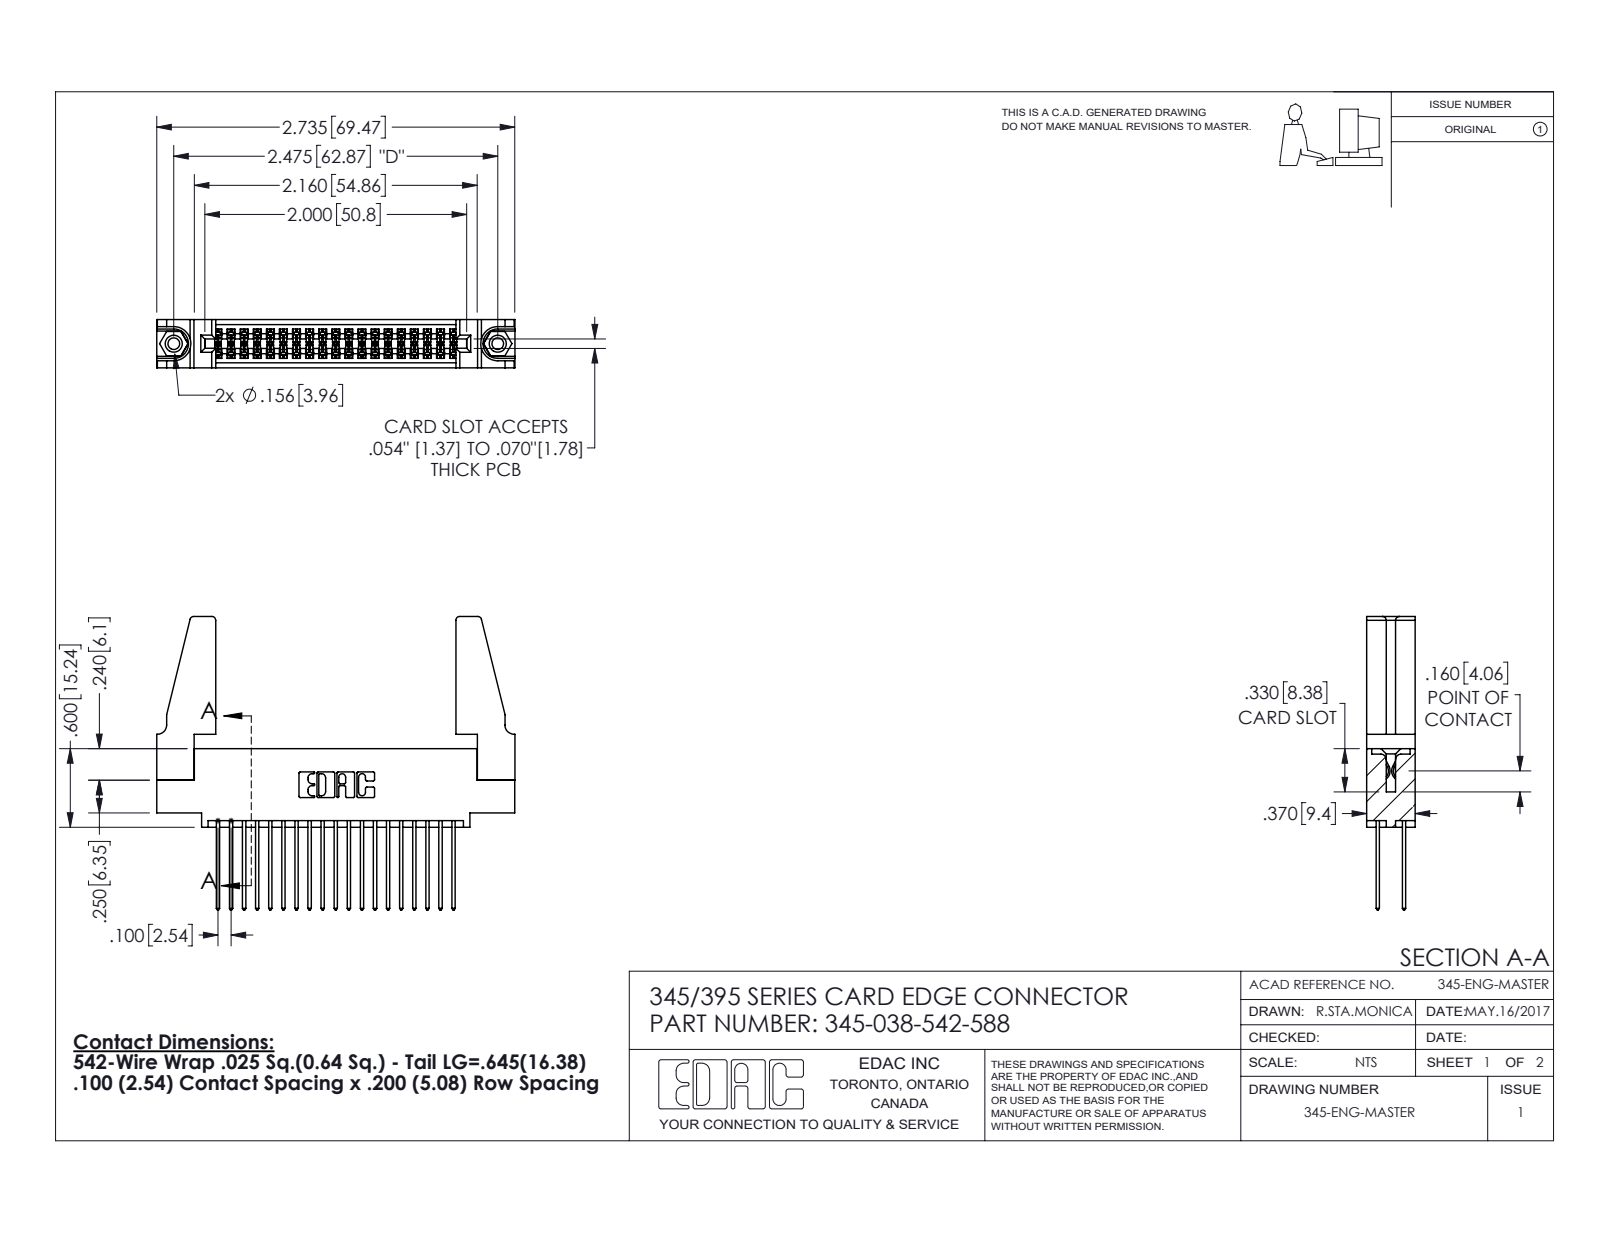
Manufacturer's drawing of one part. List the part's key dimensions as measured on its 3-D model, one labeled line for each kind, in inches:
Part name (STEP PRODUCT): 345-250-001_345-250-001-102; 345-220-078_345-220-088; 345 Part_0.110 Offset - 0.156 Dia-TH; 345-038-542-588 (+1 more)
STEP written by: SolidWorks 2016 (CONFIG_CONTROL_DESIGN)
Units: inches
Bodies: 43 solids, 2154 faces (1410 planar, 728 cylindrical, 16 other)
Overall size (bounding box): 2.736 × 2.242 × 0.37
Volume: 0.604 in³ · Surface area: 20.79 in²
Round holes (diameter × count): ⌀0.089 ×2, ⌀0.125 ×2, ⌀0.156 ×2, ⌀0.064 ×1
Round bosses / shafts (diameter × count): ⌀0.155 ×2
Partial cylindrical surfaces — rounded edges, fillets, slot ends (radius × count): R0.006 ×57, R0.01 ×38, R0.01 ×22, R0.03 ×8, R0.007 ×6, R0.031 ×6, R0.026 ×3, R0.014 ×2
Main face-to-face distances: 0.072, 0.298, 0.37, 0.2, 0.098, 0.272, 0.025, 0.225, 0.175, 0.148
Hole centre spacings: 0.27, 2.241, 2.475
